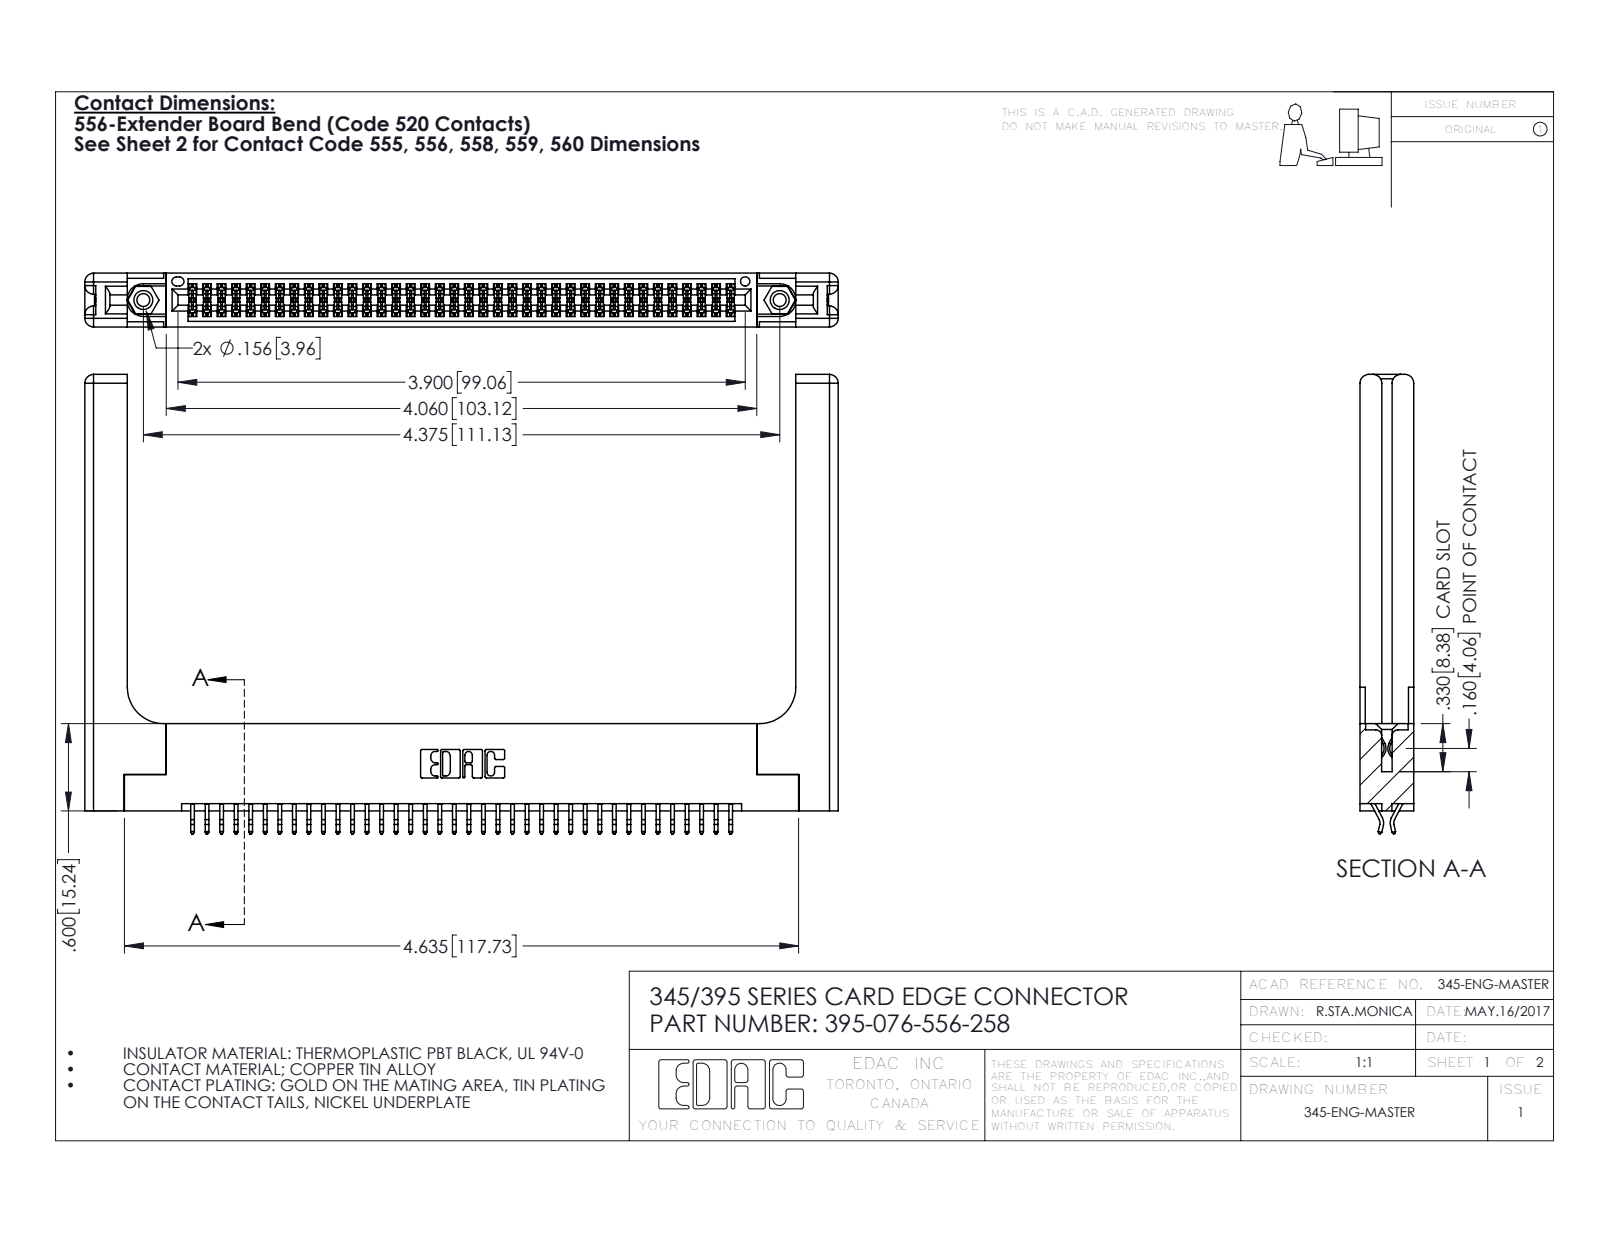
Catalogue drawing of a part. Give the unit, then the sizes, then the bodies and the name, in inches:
Units: inches
Overall size (bounding box): 5.179 × 3.157 × 0.37
Round holes (diameter × count): ⌀0.089 ×2, ⌀0.125 ×2, ⌀0.156 ×2, ⌀0.064 ×1
Round bosses / shafts (diameter × count): ⌀0.155 ×2
Partial cylindrical surfaces — rounded edges, fillets, slot ends (radius × count): R0.006 ×114, R0.01 ×22, R0.06 ×16, R0.007 ×6, R0.031 ×6, R0.026 ×3, R0.01 ×2, R0.014 ×2
Main face-to-face distances: 0.072, 0.37, 0.298, 0.2, 0.025, 0.098, 0.272, 0.225, 0.148, 0.15
Hole centre spacings: 0.27, 4.139, 4.375
Volume: 1.295 in³ · Surface area: 36.8 in²
Bodies: 81 solids, 4638 faces (3040 planar, 1538 cylindrical, 60 other)
Part name (STEP PRODUCT): 345-292-001_556 Tail; 345-220-058_345-220-058; 395-076-556-258; 345-250-001_345-250-001-102 (+1 more)
STEP written by: SolidWorks 2016 (CONFIG_CONTROL_DESIGN)
